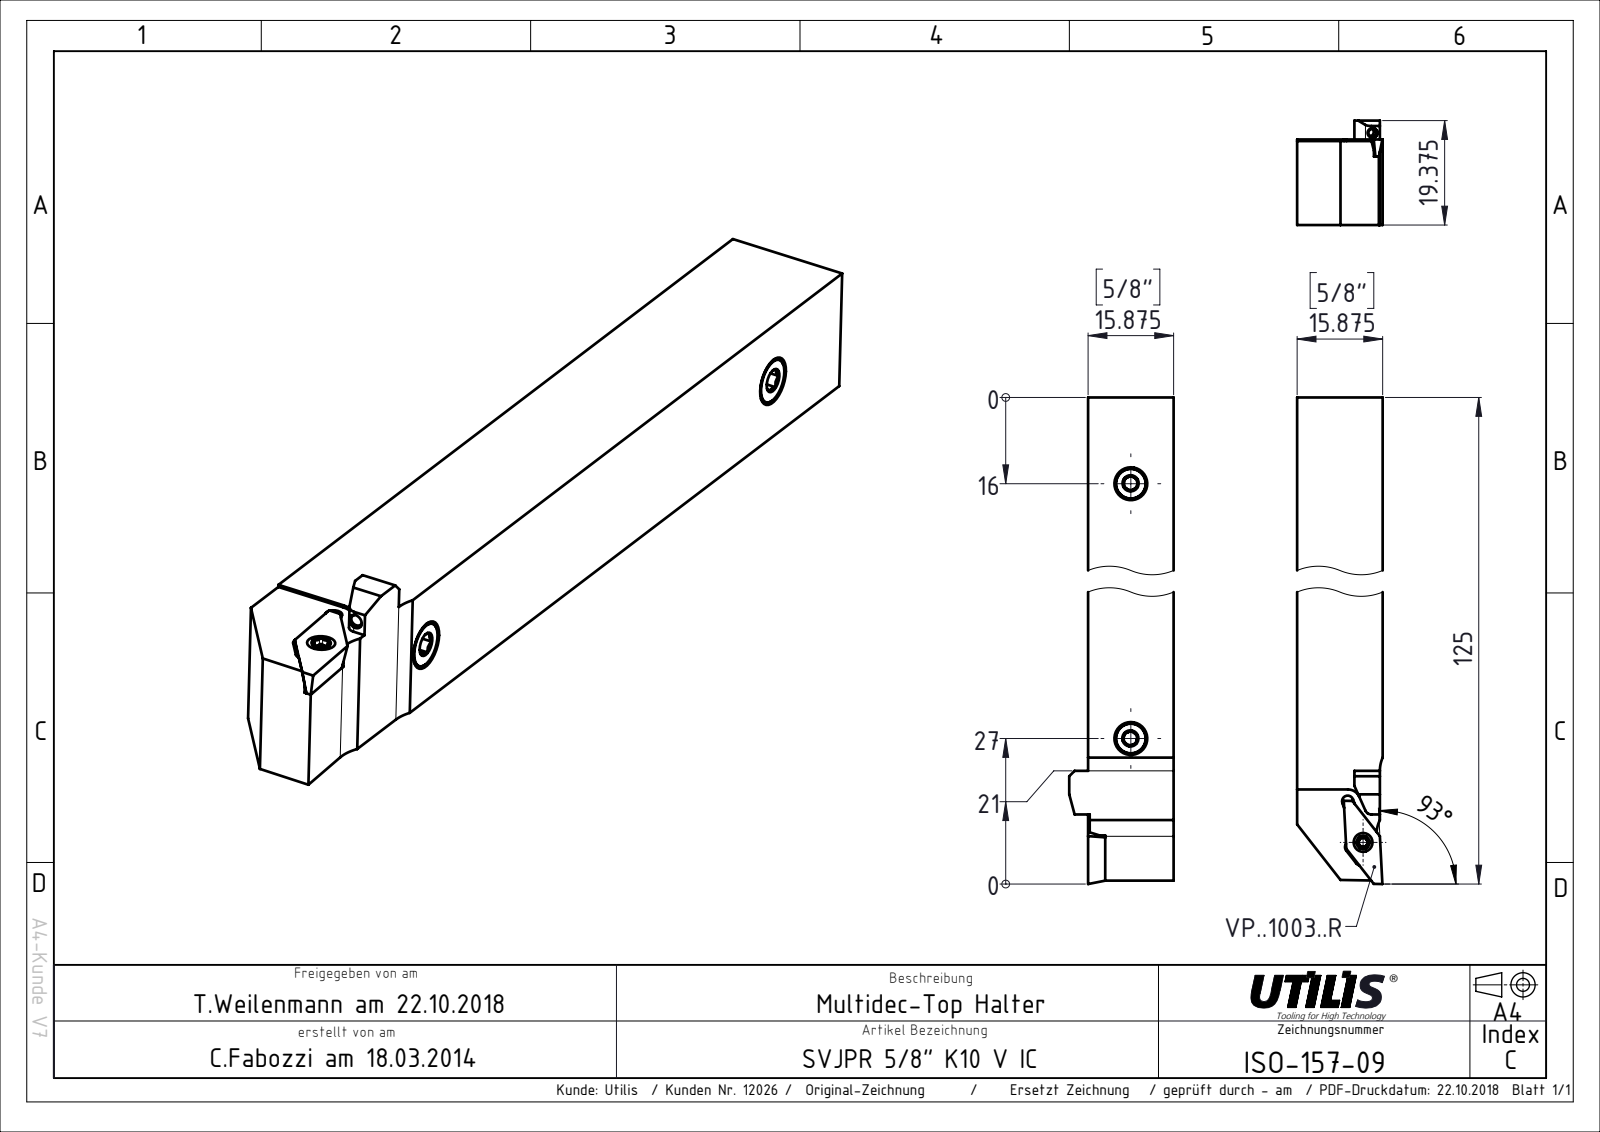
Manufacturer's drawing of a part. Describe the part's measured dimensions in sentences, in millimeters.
The part is named "ISO-157-09". Its 3-D file was written by "SolidWorks 2015 (AUTOMOTIVE_DESIGN)". It is 1 solid with 72 faces: 59 planar, 9 cylindrical and 4 other. Overall it measures 128.3 by 19.38 by 16.07 millimeters. Its volume is 30 970 cubic millimeters and its surface area 8 607 square millimeters. Round bosses or shafts: 1 of diameter 14. Partial cylindrical surfaces (rounded edges, fillets, slot ends): 3 of radius 1.05, 2 of radius 6.1, 1 of radius 2.3. The main face-to-face distances are 15.88, 15.61, 15.58, 3.3, 5, 19.38, 3.8, 3.5, 12.7, 2.88.
